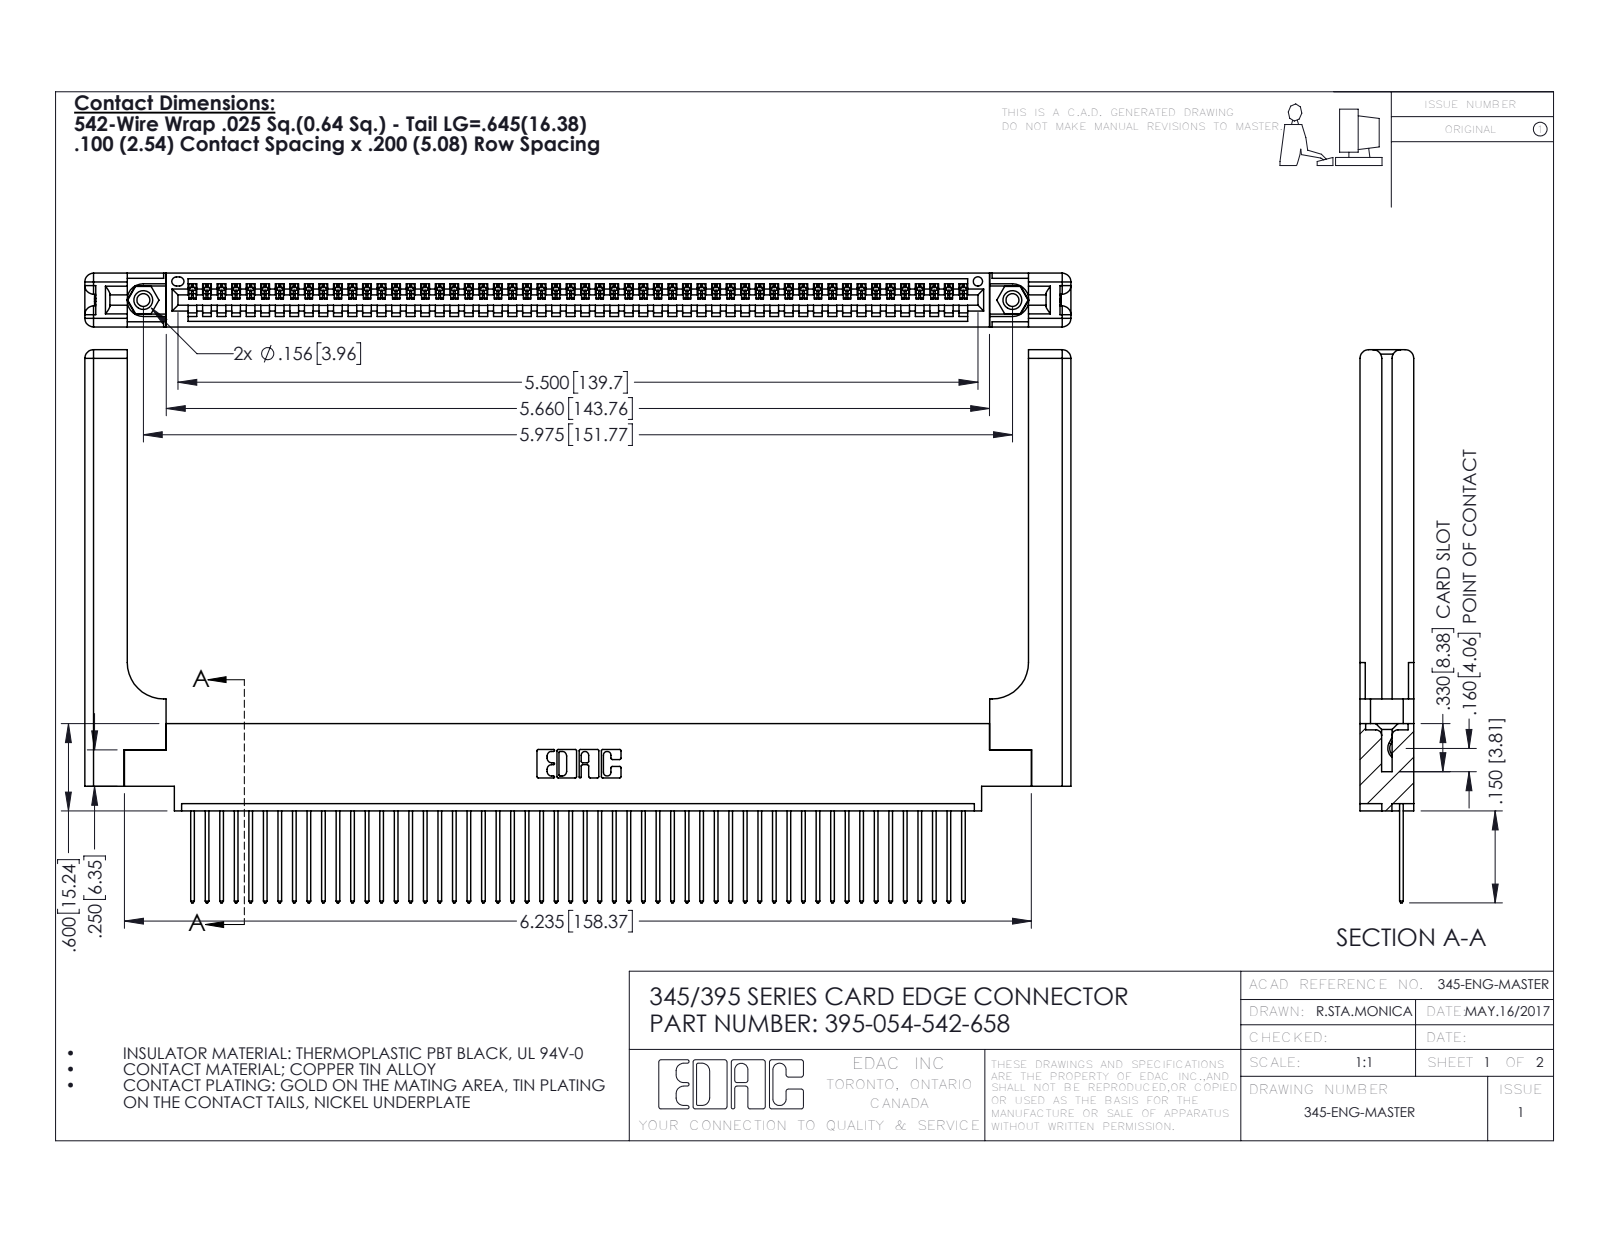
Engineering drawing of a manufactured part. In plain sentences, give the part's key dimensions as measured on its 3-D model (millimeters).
The part is named "395-054-542-658; 345-220-058_345-220-058; 345-250-001_345-250-001-102; 345 Part_0.170 Offset - 0.156 Dia-TH (+1 more)". Its 3-D file was written by "SolidWorks 2016 (CONFIG_CONTROL_DESIGN)". It is 59 solids with 3518 faces: 2392 planar, 1066 cylindrical and 60 other. Overall it measures 172.2 by 96.6 by 9.4 millimeters. Its volume is 24 960 cubic millimeters and its surface area 28 230 square millimeters. Round holes: 2 of diameter 2.3, 2 of diameter 3.2, 2 of diameter 4, 1 of diameter 1.6. Round bosses or shafts: 2 of diameter 3.9. Partial cylindrical surfaces (rounded edges, fillets, slot ends): 108 of radius 0.2, 108 of radius 0.3, 22 of radius 0.3, 16 of radius 1.5, 6 of radius 0.2, 6 of radius 0.8, 3 of radius 0.7, 2 of radius 0.8. The main face-to-face distances are 1.8, 9.4, 7.6, 2.5, 6.9, 0.6, 5.1, 5.7, 3.8, 3.8. The hole center spacings are 6.9, 145.8, 151.8.
